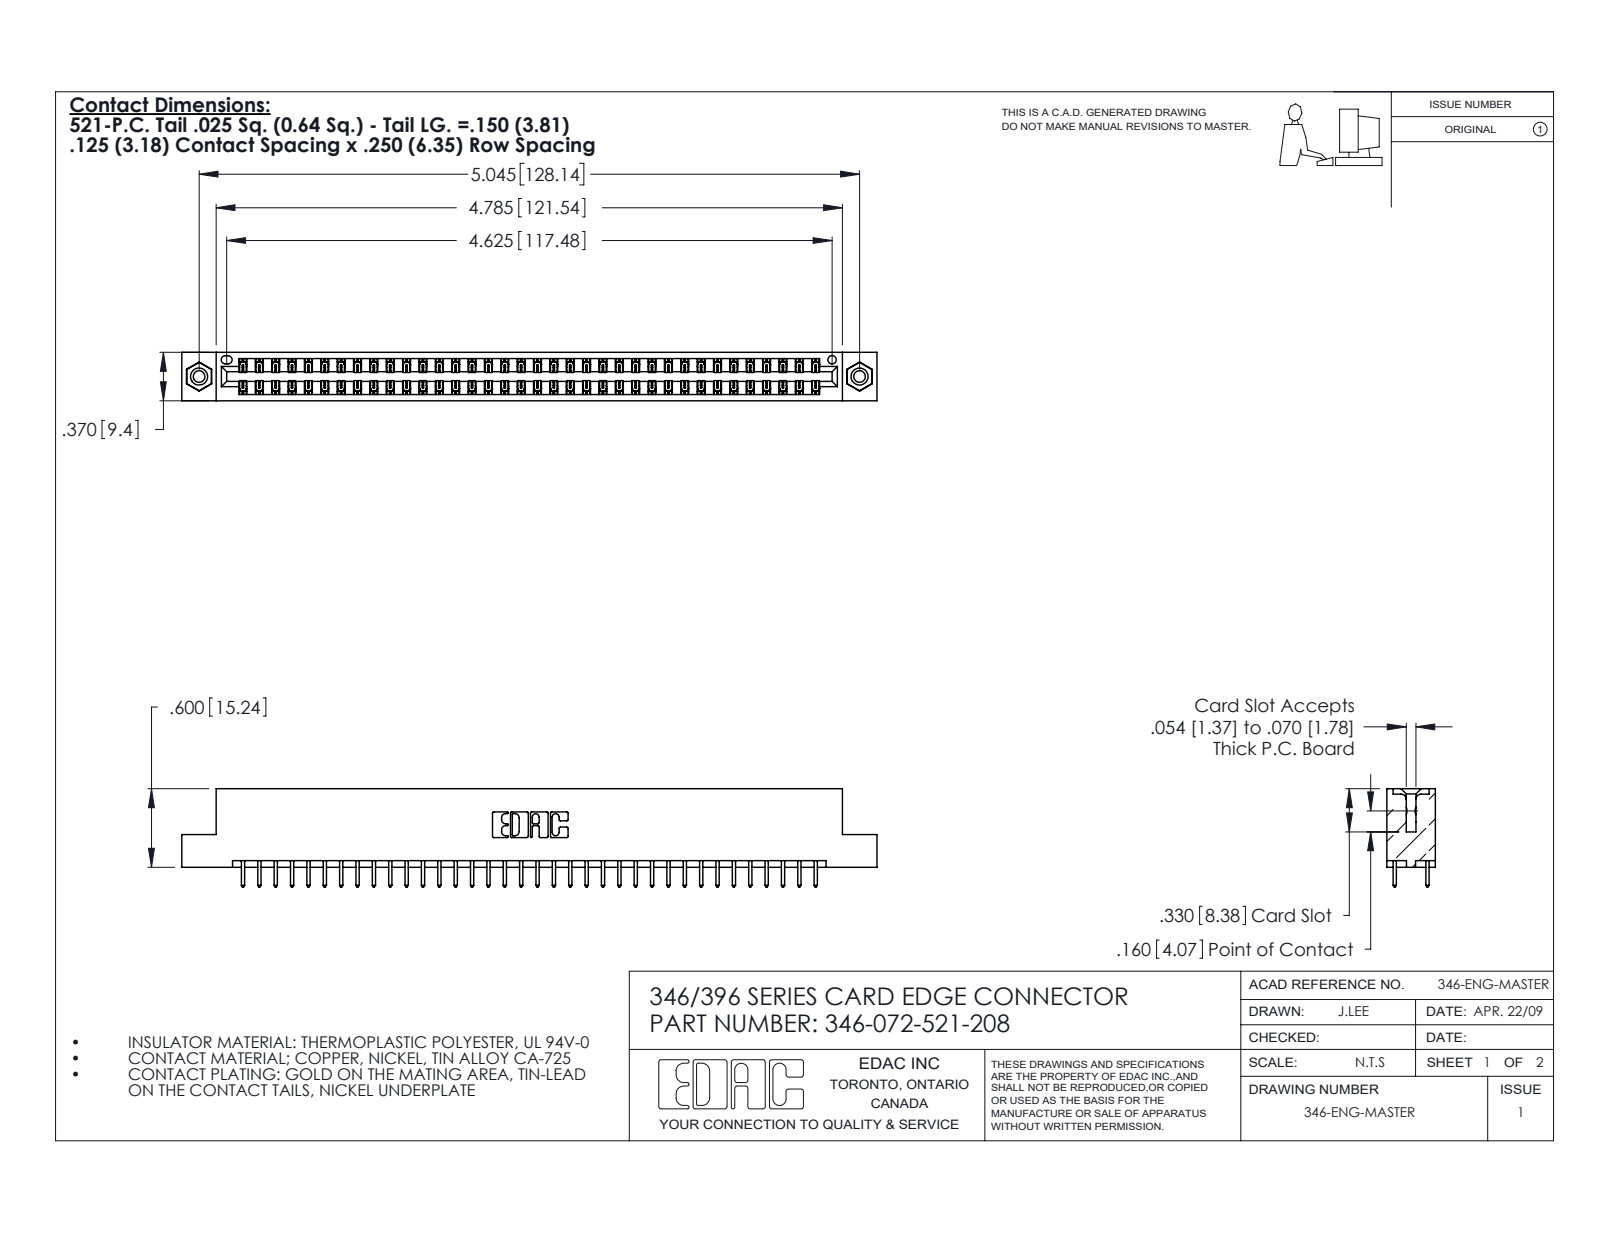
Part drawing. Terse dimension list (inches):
name: 346 Part_Flush Mounting Lugs - 0.156 Dia-TI; 346-072-521-208; 345-250-001_345-250-003-102; 345-292-001_345-293-121
written by: SolidWorks 2020 (CONFIG_CONTROL_DESIGN)
unit: in
bodies: 75 solids, 3926 faces (2628 planar, 1282 cylindrical, 16 other)
size: 5.31 × 0.75 × 0.37
volume: 0.798 in³; area: 27.42 in²
holes: 2× ⌀0.089, 2× ⌀0.125, 2× ⌀0.156, 1× ⌀0.064
bosses: 2× ⌀0.155
rounds: 108× R0.006, 72× R0.01, 22× R0.01, 6× R0.007, 6× R0.031, 3× R0.026, 2× R0.014, 2× R0.022
face distances: 0.048, 0.322, 0.25, 0.37, 0.072, 0.298, 0.025, 0.275, 0.148, 0.222
hole spacings: 0.246, 4.836, 5.045
